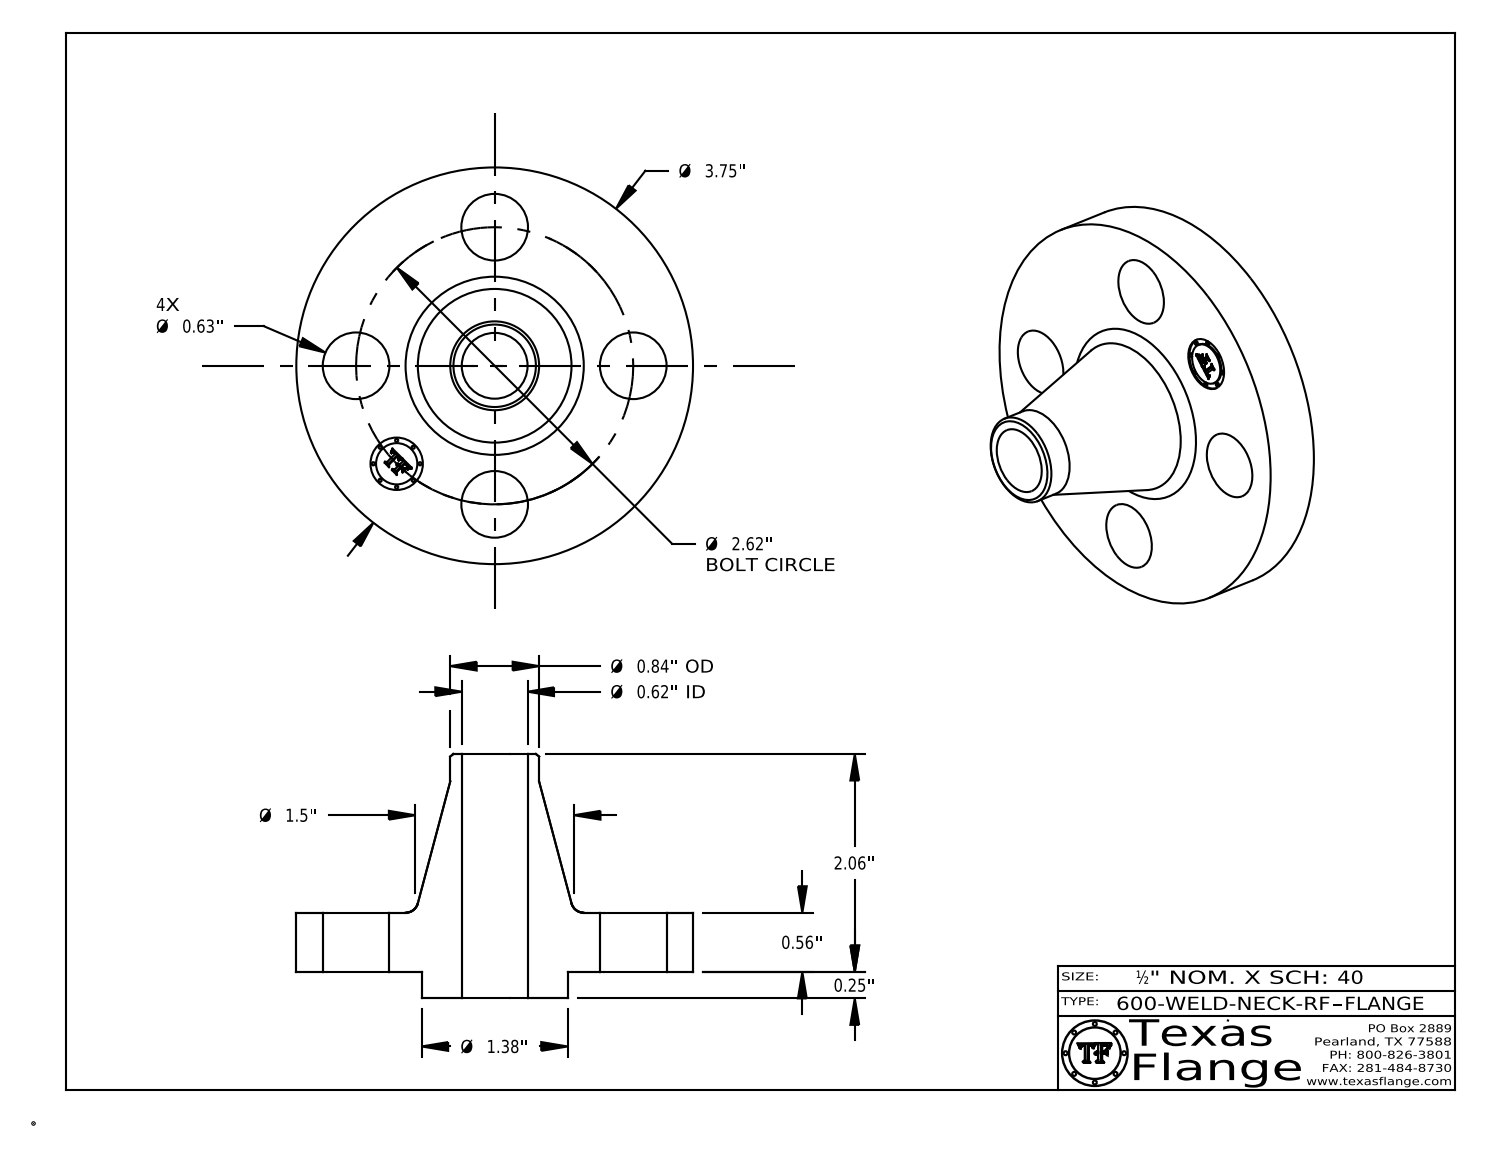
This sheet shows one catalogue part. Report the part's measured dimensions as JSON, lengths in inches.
{"part_name": "600-WELD-NECK-RF", "step_written_by": "CATIA V5 STEP AP214 (AUTOMOTIVE_DESIGN)", "units": "inches", "bodies": {"solids": 1, "faces": 411, "planar": 369, "cylindrical": 36, "other": 6}, "overall_size": [3.75, 3.75, 2.31], "volume_in3": 6.677, "surface_area_in2": 39.73, "round_holes": [[0.63, 4], [0.495, 1], [0.622, 1]], "round_bosses_or_shafts": [[0.03, 8], [3.75, 1], [1.38, 1], [0.84, 1], [0.39, 1]], "face_to_face_distances": [0.56, 0.25, 0.81, 2.31, 2.06, 1.5, 0.795, 0.545, 0.015, 1.515], "hole_center_spacings": [1.31, 1.852, 1.003, 2.42, 2.62, 1.31]}
